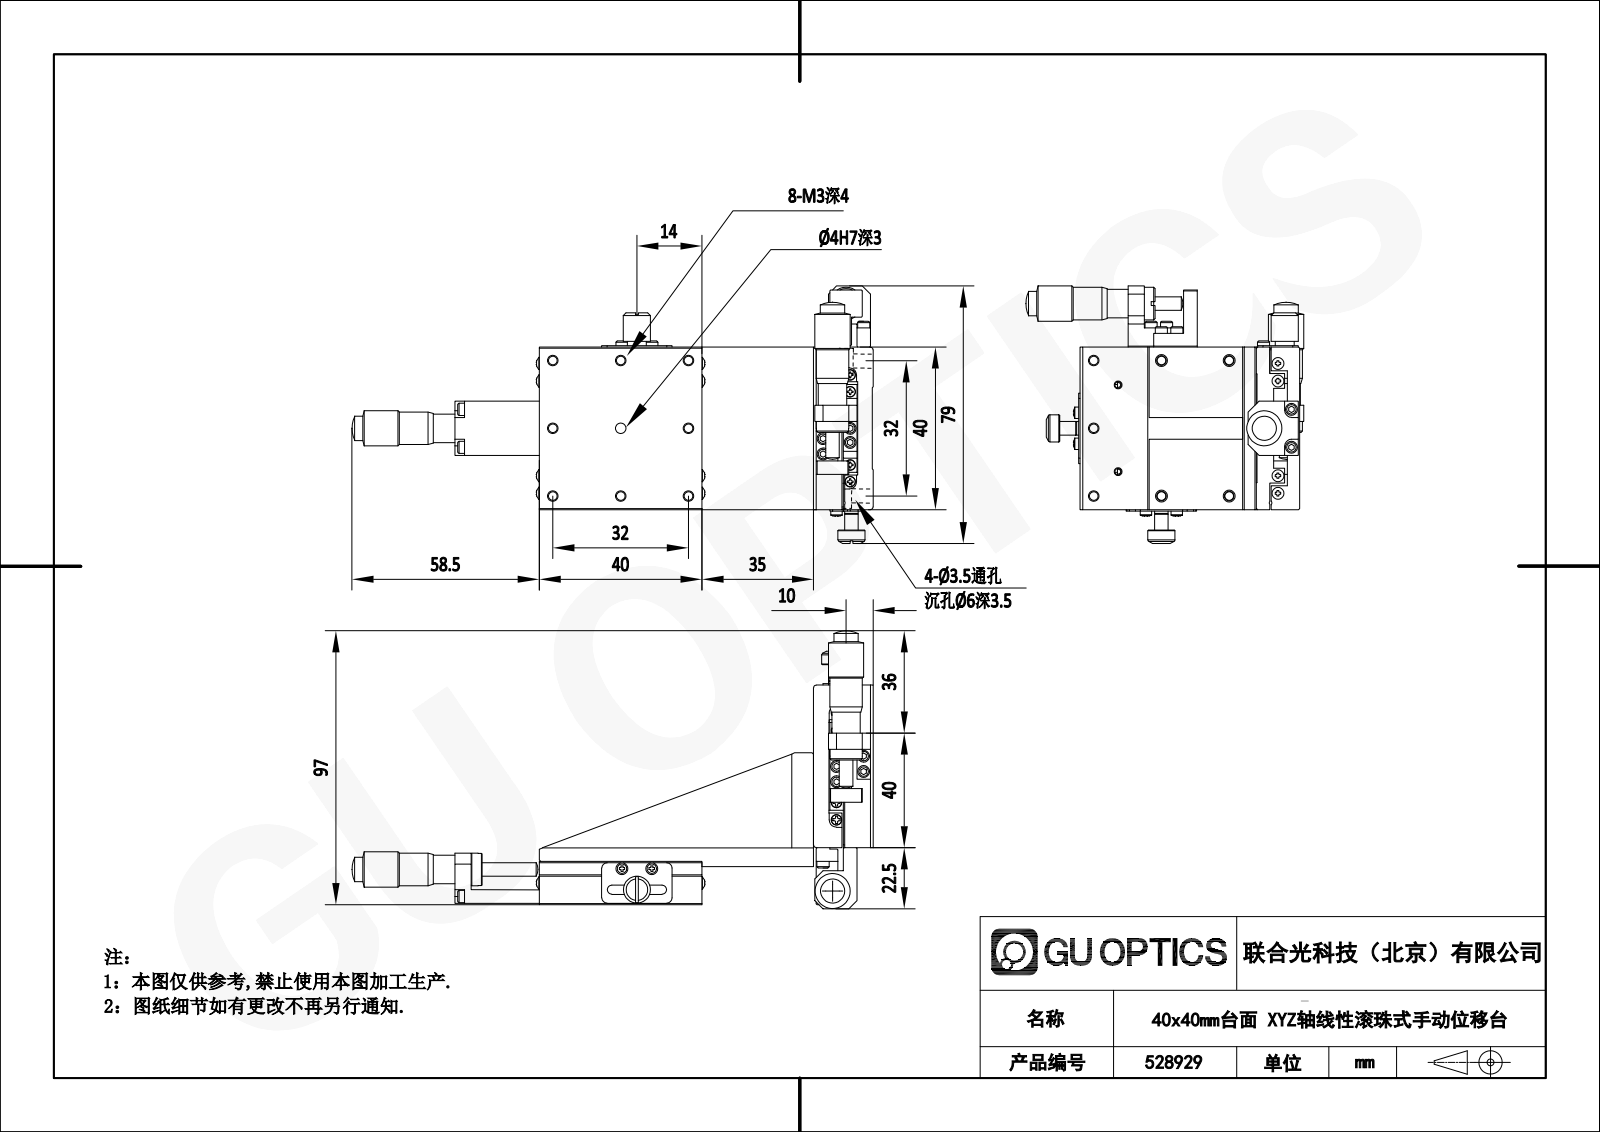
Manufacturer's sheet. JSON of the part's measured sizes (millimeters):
{"part_name": "1724657666795", "step_written_by": "Forface 3D 2012 (AUTOMOTIVE_DESIGN)", "units": "millimeters", "bodies": {"solids": 8, "faces": 1238, "planar": 642, "cylindrical": 376, "other": 220}, "overall_size": [155.51, 98.51, 79.01], "volume_mm3": 106667, "surface_area_mm2": 58248, "round_holes": [[2.46, 10], [3.5, 8], [6, 8], [2.46, 6], [2.85, 6], [2.01, 4], [5, 3], [9, 3], [3.96, 2], [4, 2], [3.24, 1]], "round_bosses_or_shafts": [[4.5, 16], [4.2, 4], [4, 4], [13, 3], [12, 3], [12, 3], [10.5, 3], [10, 3]], "partial_cylinders_radius": [[0.25, 34], [0.1, 24], [2, 12], [0.5, 8], [1, 8], [1.65, 4], [1.4, 2], [1.75, 2]], "face_to_face_distances": [5, 16, 5.5, 11, 10.5, 0.5, 5.7, 40, 10.3, 6], "hole_center_spacings": [16, 22.63, 35.78, 32, 45.25, 20, 32.25, 46.82]}
